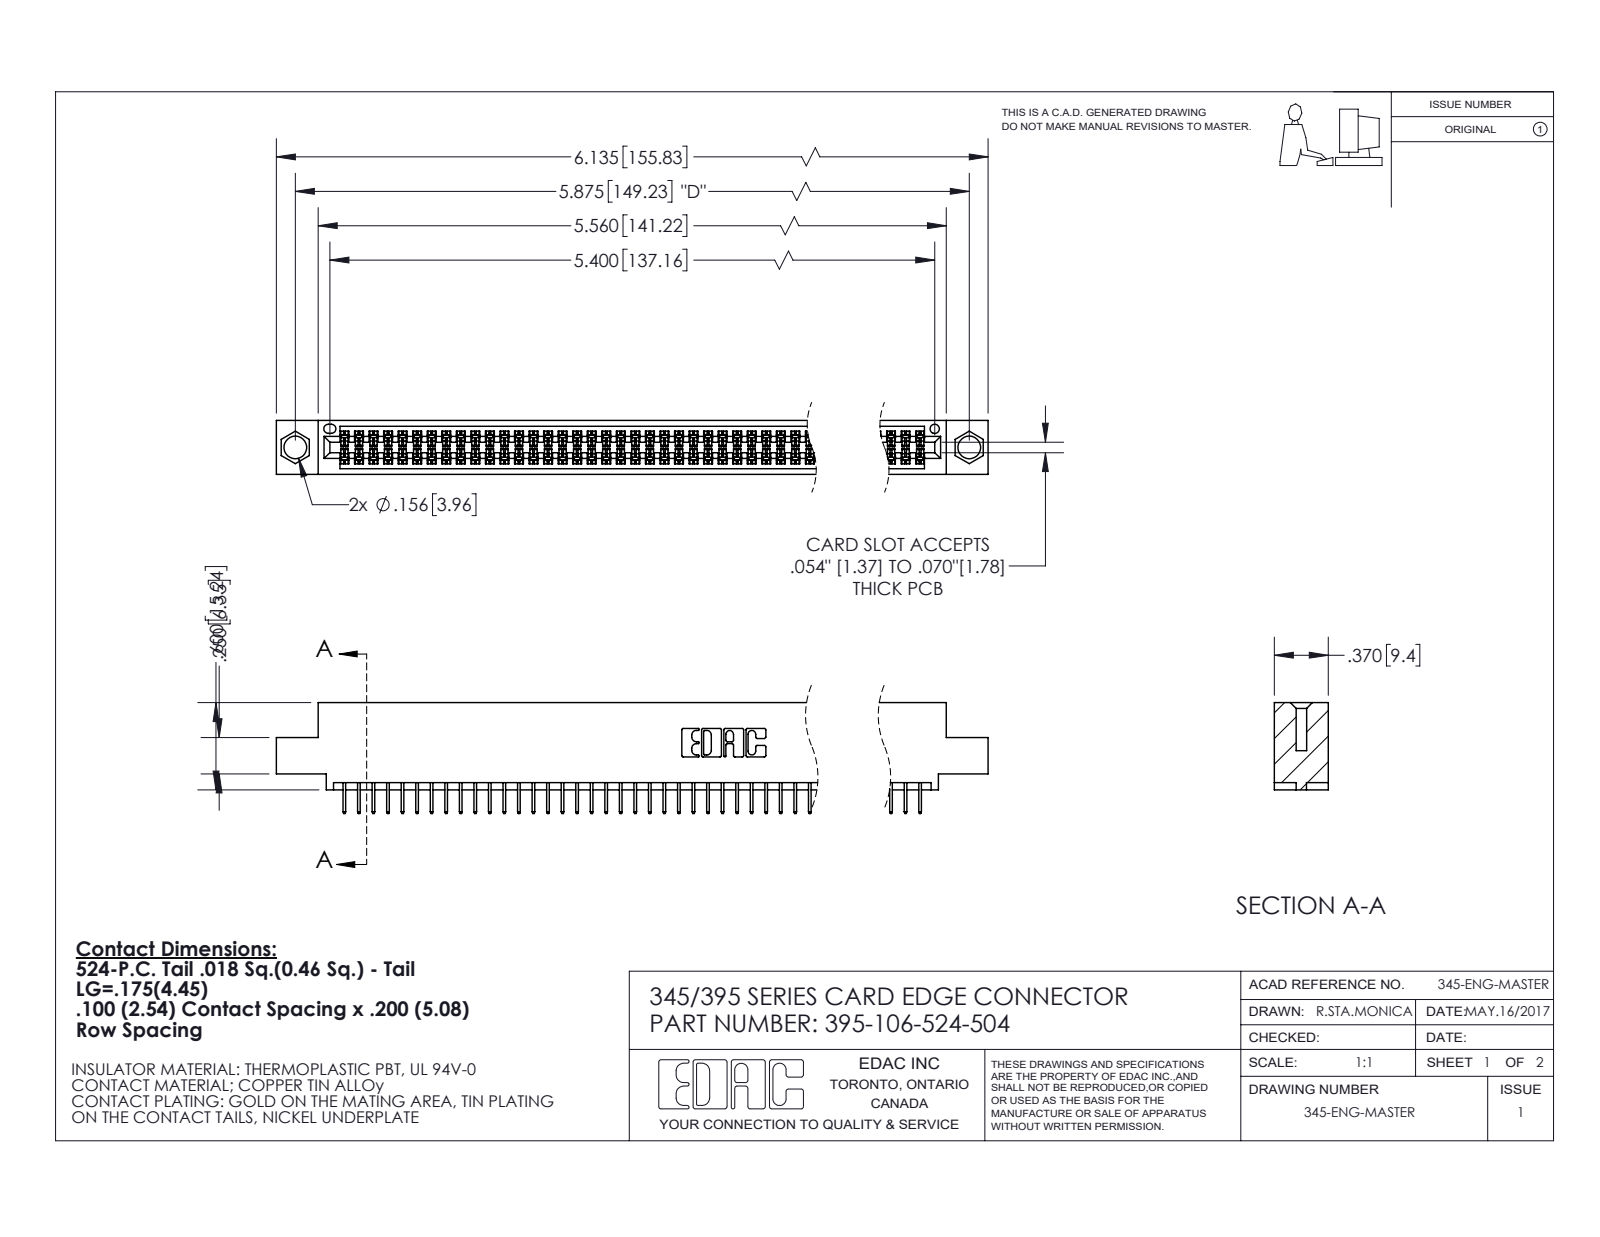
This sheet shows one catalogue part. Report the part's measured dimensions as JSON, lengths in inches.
{"part_name": "345 Part_0.110 Offset - 0.156 Dia-TI; 345-292-001_345-293-124; 395-106-524-504", "step_written_by": "SolidWorks 2020 (CONFIG_CONTROL_DESIGN)", "units": "inches", "bodies": {"solids": 107, "faces": 5868, "planar": 4232, "cylindrical": 1636, "other": 0}, "overall_size": [6.135, 0.762, 0.37], "volume_in3": 0.909, "surface_area_in2": 33.73, "round_holes": [[0.156, 2], [0.064, 1]], "partial_cylinders_radius": [[0.006, 212], [0.01, 22], [0.007, 6], [0.031, 6], [0.026, 3], [0.014, 2], [0.019, 2], [0.022, 2]], "face_to_face_distances": [0.072, 0.298, 0.2, 0.37, 0.098, 0.272, 0.025, 0.225, 0.072, 0.175], "hole_center_spacings": [0.27, 5.639, 5.875]}
